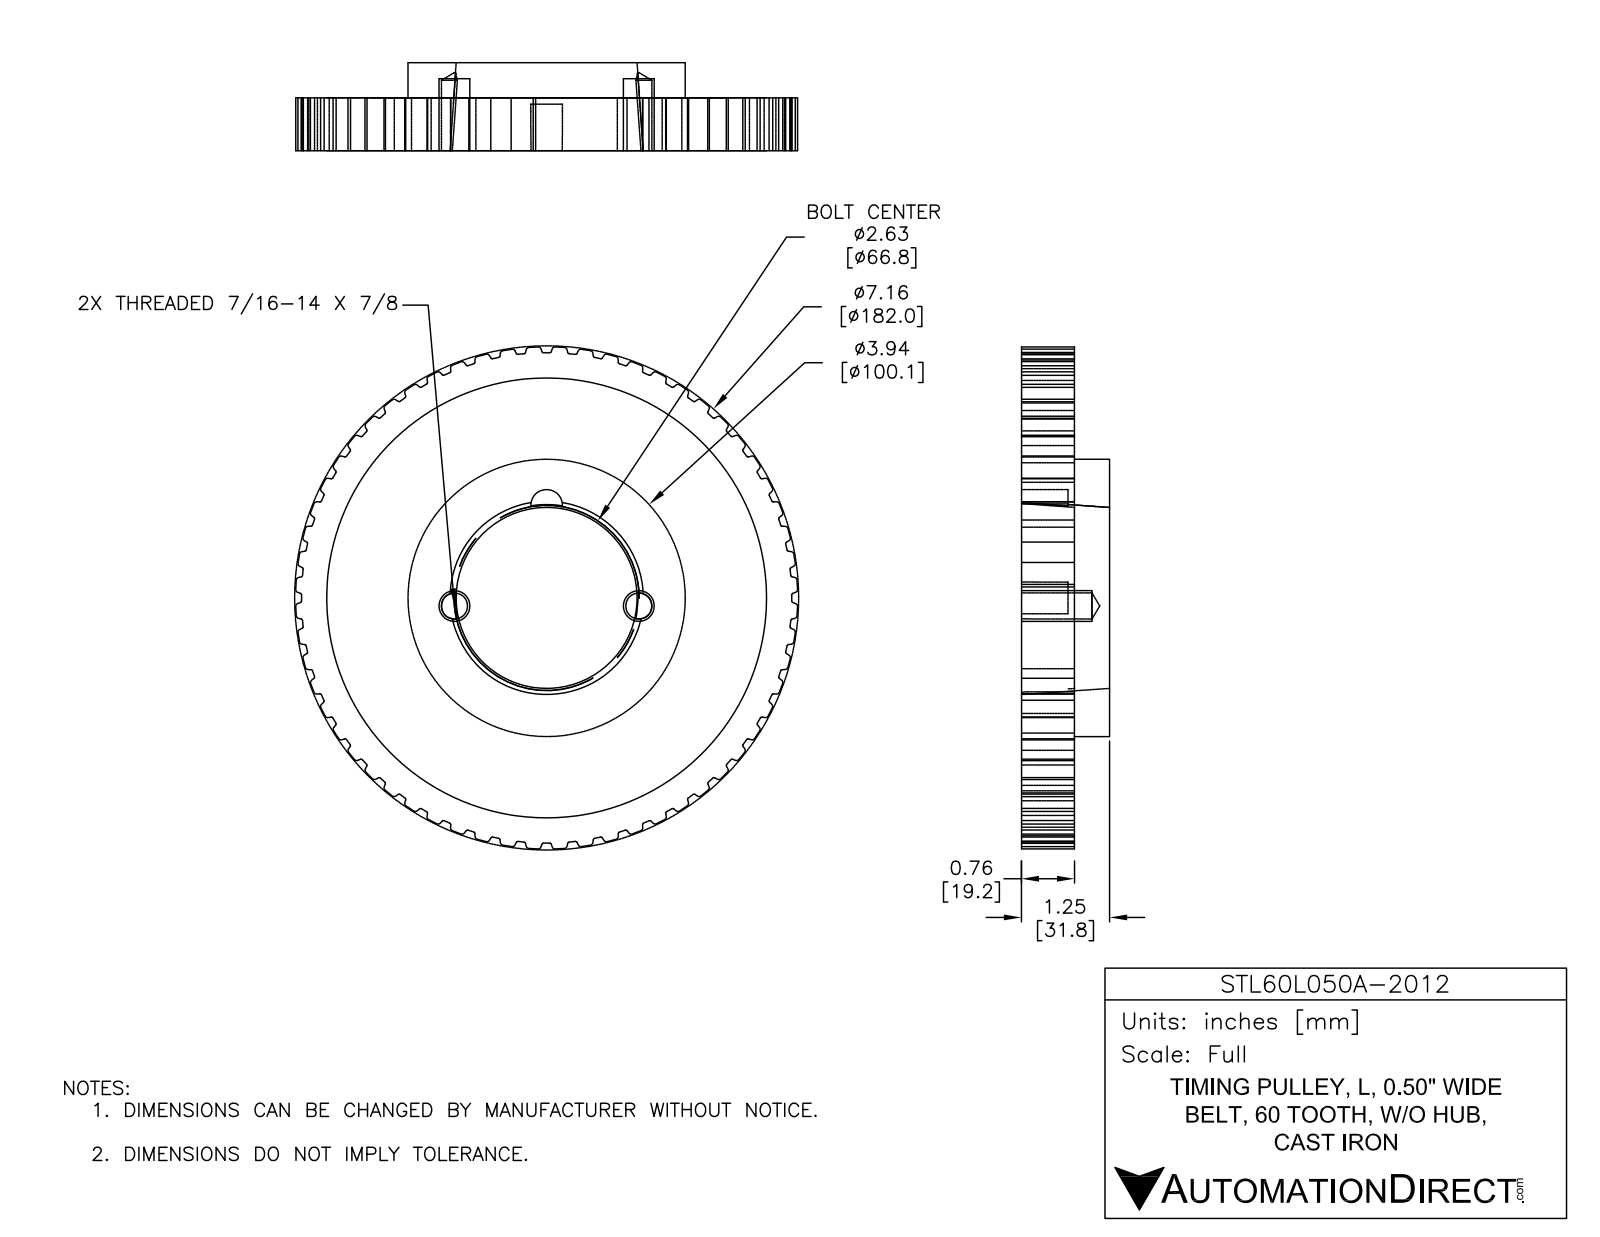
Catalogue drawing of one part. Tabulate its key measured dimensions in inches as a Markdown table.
| quantity | value |
| --- | --- |
| part name | STL60L050A-2012 |
| STEP written by | SolidWorks 2018 (AUTOMOTIVE_DESIGN) |
| units | inches |
| bodies | 1 solid, 554 faces (187 planar, 365 cylindrical, 2 other) |
| overall size | 7.126 × 7.126 × 1.252 |
| volume | 25.6 in³ |
| surface area | 110.7 in² |
| round holes (diameter × count) | 6.252 × 1 |
| round bosses / shafts (diameter × count) | 3.941 × 1, 3.94 × 1 |
| partial cylindrical surfaces (radius × count) | 0.015 × 120, 0.02 × 120, 0.185 × 2, 0.225 × 1, 3.563 × 1 |
| main face-to-face distances | 0.597, 0.079, 0.676, 0.755, 0.291, 0.37, 0.967, 1.046, 1.252, 0.961 |
